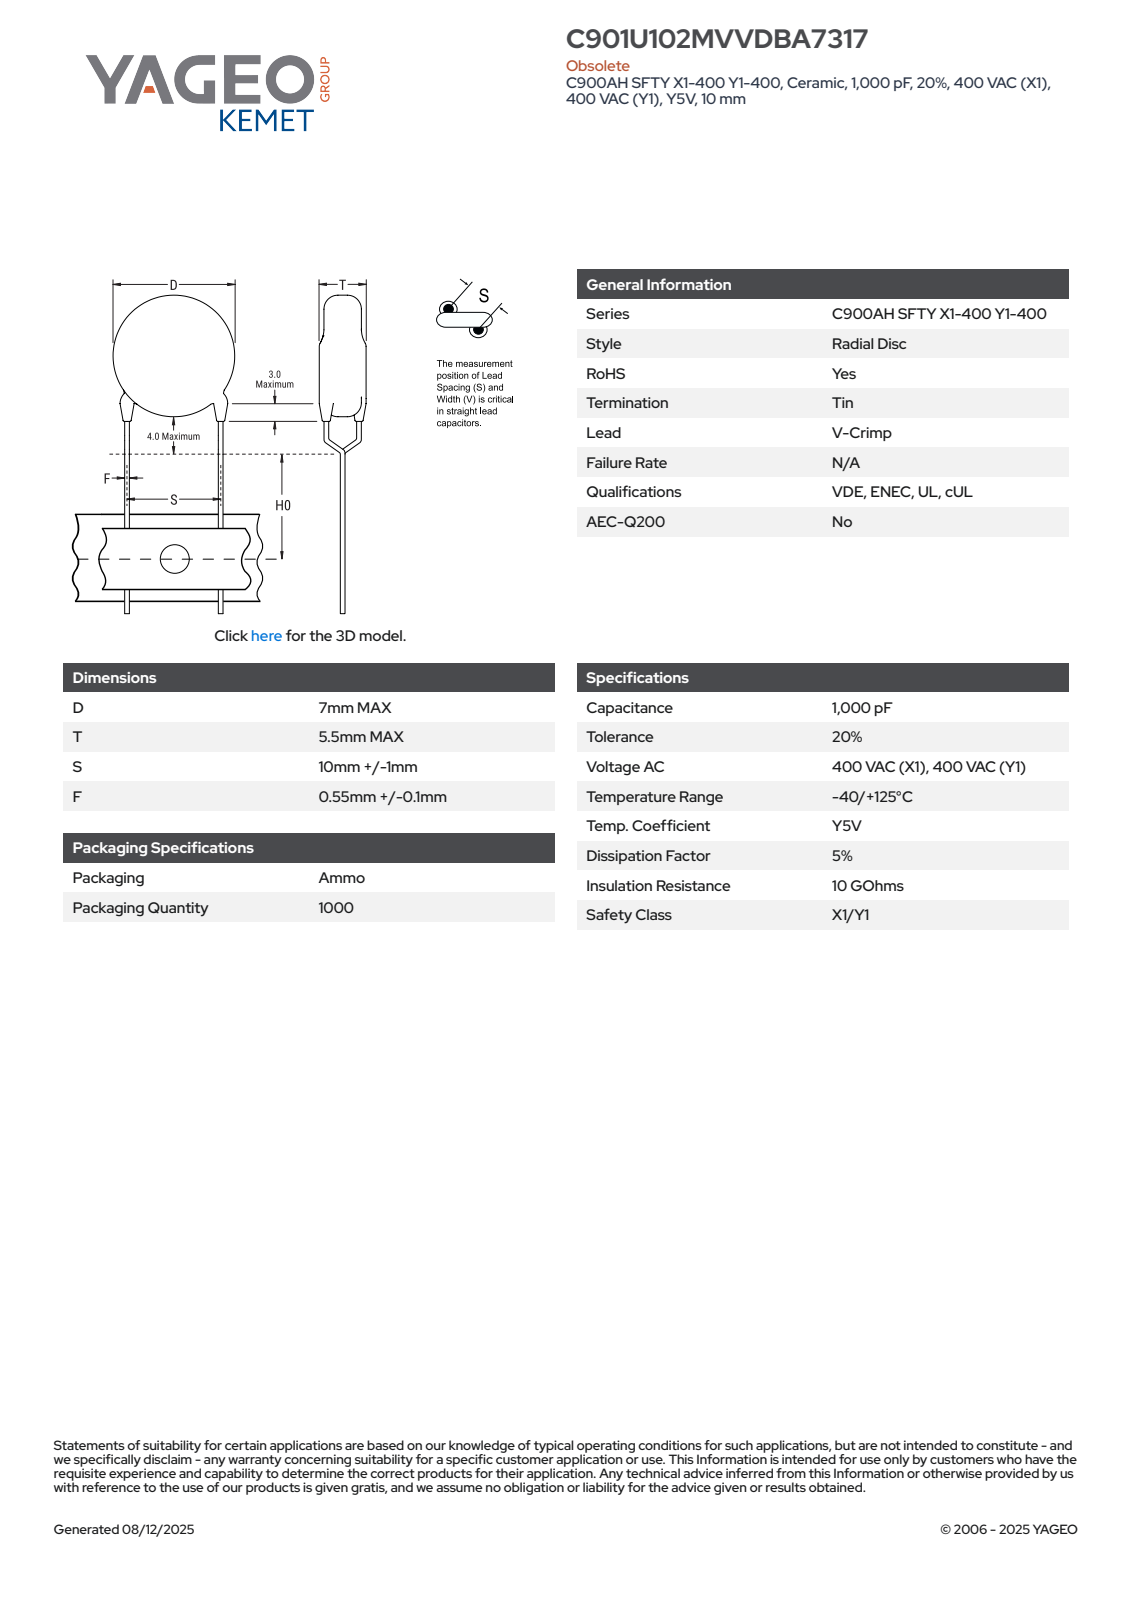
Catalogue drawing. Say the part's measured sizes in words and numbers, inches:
The part is named "CCD_VCC900_D7T5.5S10LL20F0.65". Its 3-D file was written by "SolidWorks 2014 (AUTOMOTIVE_DESIGN)". It is 5 solids with 93 faces: 65 planar, 16 cylindrical and 12 other. Overall it measures 1.213 by 0.419 by 0.217 inches. Its volume is 0.014 cubic inches and its surface area 0.463 square inches. Round bosses or shafts: 6 of diameter 0.026, 1 of diameter 0.276. The main face-to-face distances are 0.217, 0.902, 0.036, 1.093, 0.191, 1.057, 0.155, 0.146, 0.013, 0.074.
